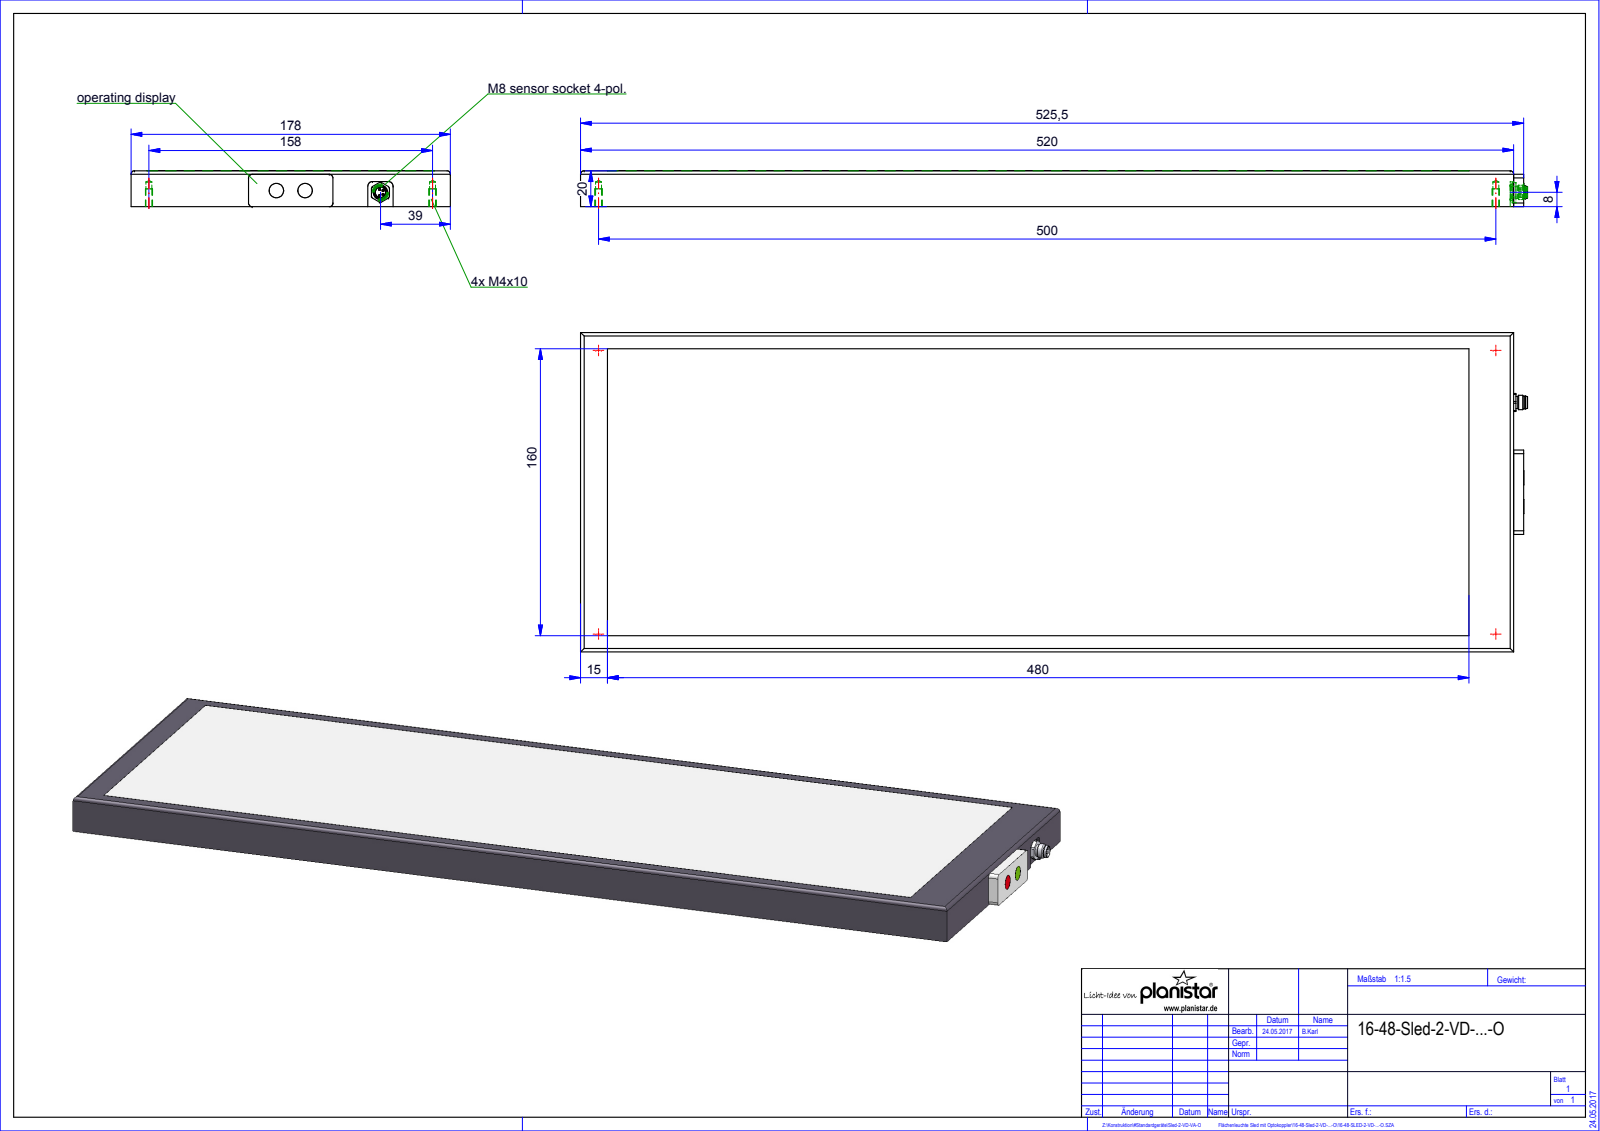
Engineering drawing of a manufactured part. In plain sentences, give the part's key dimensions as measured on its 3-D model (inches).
The part is named "Root; Baugruppe_Xled-2-VD; QUADER_0; 09-3391-00-04". Its 3-D file was written by "HiCAD 2015 2002.1 Build 408 (AUTOMOTIVE_DESIGN)". It is 3 solids with 89 faces: 39 planar, 37 cylindrical and 13 other. Overall it measures 20.776 by 7.008 by 0.791 inches. Its volume is 113.6 cubic inches and its surface area 334.3 square inches. Round holes: 4 of diameter 0.13, 4 of diameter 0.157, 1 of diameter 0.228. Round bosses or shafts: 4 of diameter 0.039, 3 of diameter 0.315, 1 of diameter 0.283, 1 of diameter 0.268, 1 of diameter 0.252. Partial cylindrical surfaces (rounded edges, fillets, slot ends): 8 of radius 0.079, 2 of radius 0.098, 1 of radius 0.217. The main face-to-face distances are 0.791, 0.787, 7.008, 20.472, 20.689, 0.217, 0.079, 0.083, 0.709, 20.394. The hole center spacings are 6.22, 19.685, 20.644.
